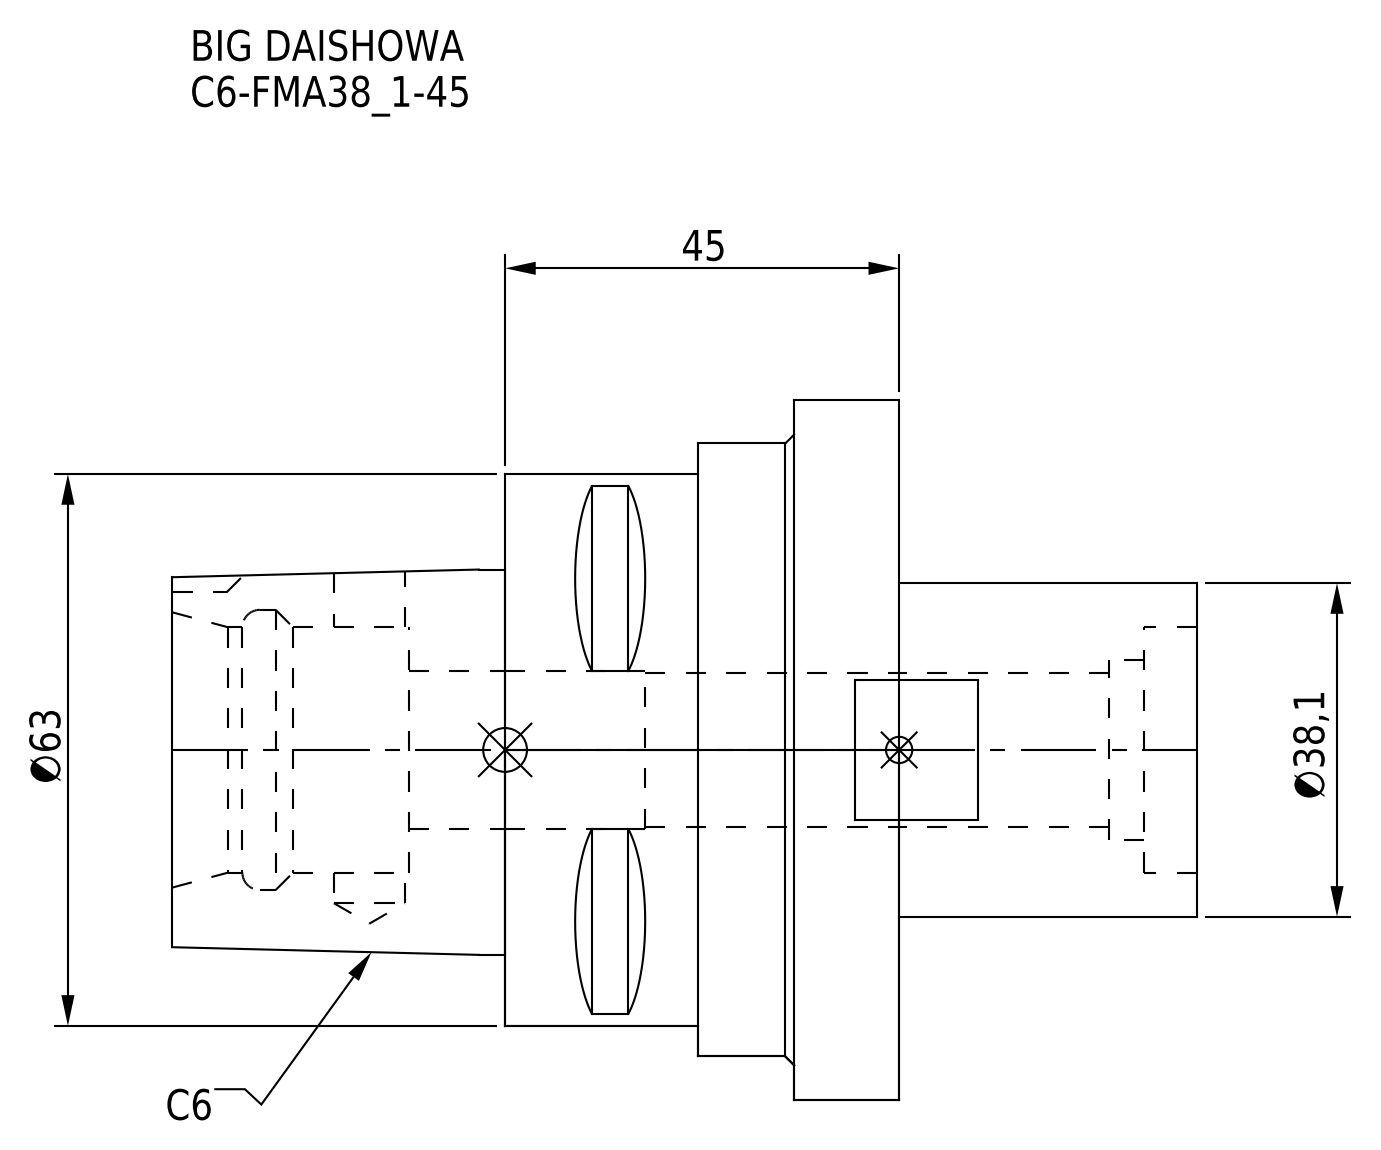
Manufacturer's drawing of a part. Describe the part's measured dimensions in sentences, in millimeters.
The part is named "C6-FMA38_1-45". Its 3-D file was written by "CREO PARAMETRIC BY PTC INC, 2016380 (AUTOMOTIVE_DESIGN)". It is 1 solid with 81 faces: 42 planar, 27 cylindrical and 12 other. Overall it measures 117 by 80 by 80 millimeters. Its volume is 226 018 cubic millimeters and its surface area 37 841 square millimeters. Round holes: 1 of diameter 8.1, 1 of diameter 17.5, 1 of diameter 18, 1 of diameter 20.5, 1 of diameter 28, 1 of diameter 32. Round bosses or shafts: 1 of diameter 80, 1 of diameter 70, 1 of diameter 63, 1 of diameter 38.1. Partial cylindrical surfaces (rounded edges, fillets, slot ends): 1 of radius 5. The main face-to-face distances are 45, 33, 11, 12, 60, 23, 22, 54, 9, 21.
